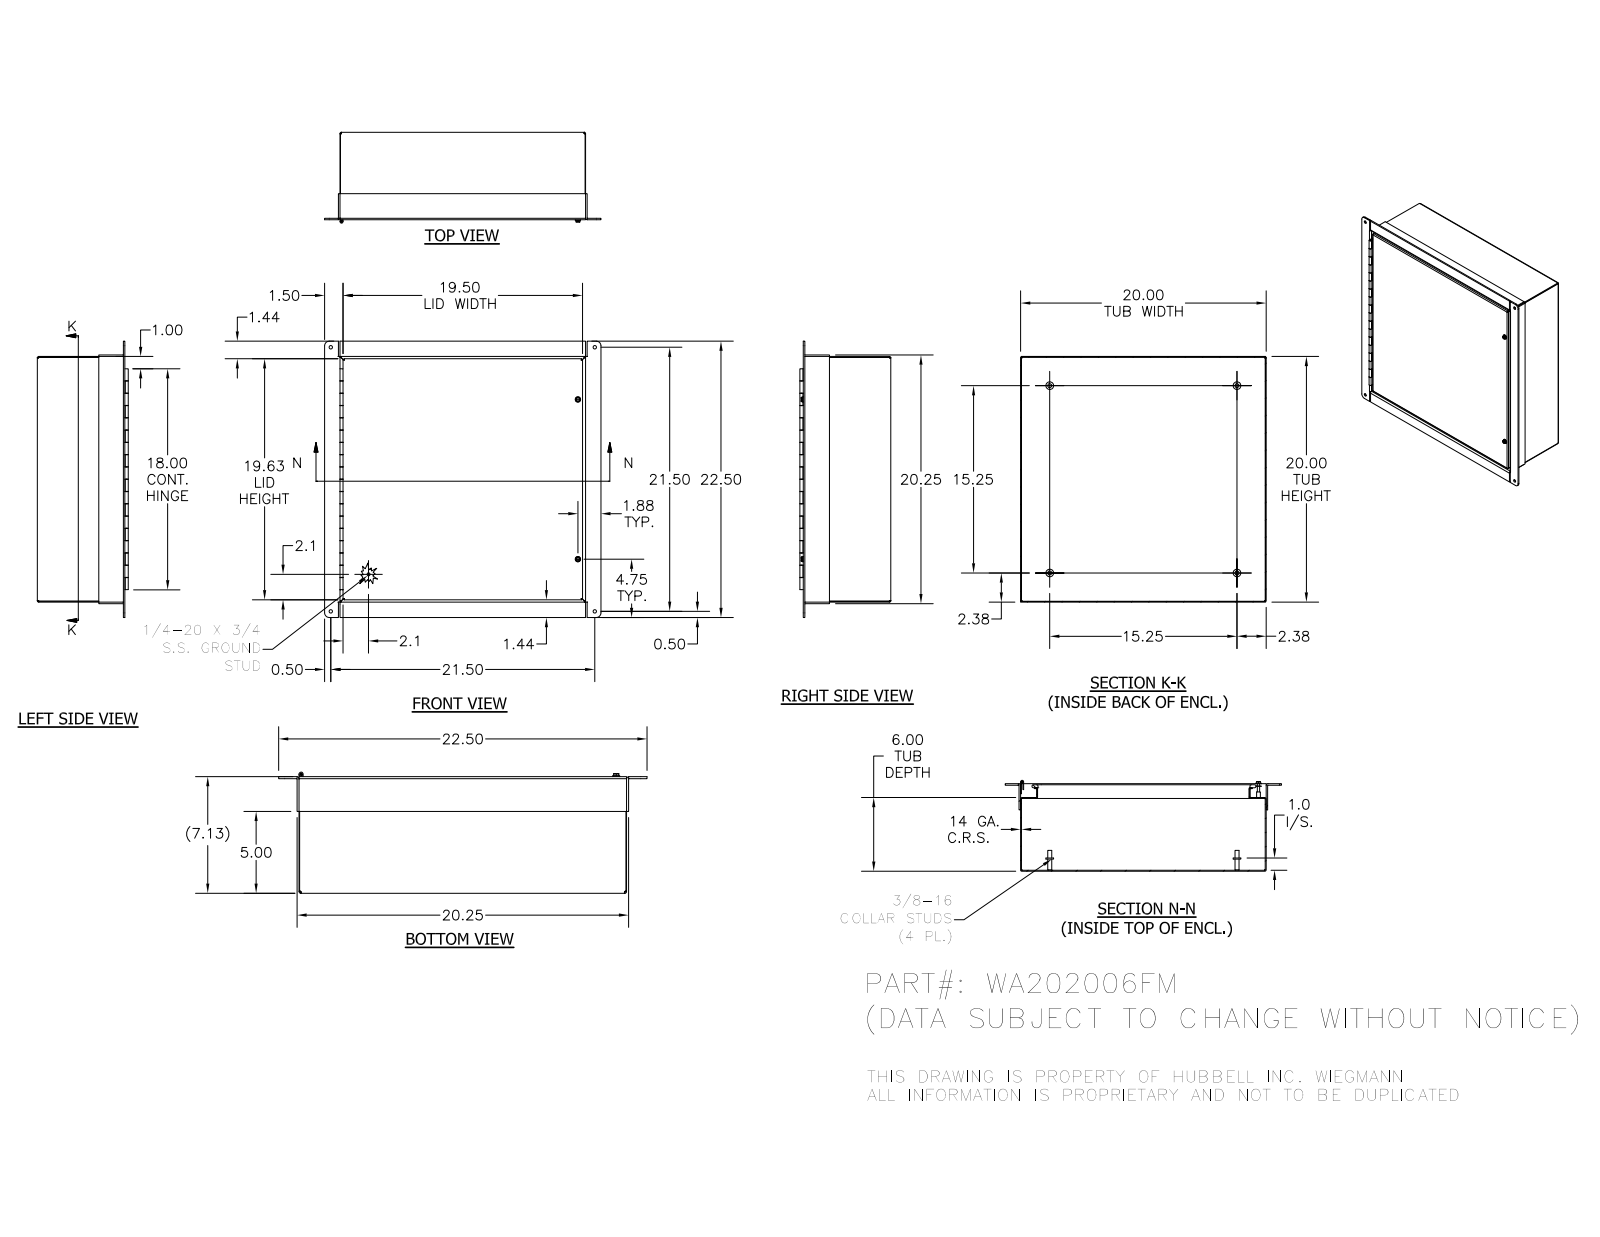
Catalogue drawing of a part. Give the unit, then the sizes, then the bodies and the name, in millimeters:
Units: millimetres
Overall size (bounding box): 571.5 × 571.5 × 187.96
Round holes (diameter × count): ⌀7.14 ×6, ⌀9.52 ×4, ⌀3.96 ×2, ⌀4.78 ×2, ⌀7.06 ×2, ⌀3.17 ×1
Round bosses / shafts (diameter × count): ⌀15.88 ×4, ⌀8.38 ×4, ⌀11.51 ×2, ⌀11.11 ×2, ⌀10.52 ×2, ⌀7.94 ×2, ⌀6.35 ×2, ⌀4.83 ×2
Partial cylindrical surfaces — rounded edges, fillets, slot ends (radius × count): R0.79 ×24, R2.67 ×20, R1.78 ×8, R3.17 ×8, R3.97 ×4, R9.53 ×4, R2.27 ×2
Main face-to-face distances: 1.88, 178.84, 506.12, 176.96, 180.72, 508, 504.24, 3.17, 150.52, 28.32
Hole centre spacings: 546.1, 113.46, 143.94, 439.54, 522.45, 673.26, 772.3, 143.95
Volume: 2 494 000 mm³ · Surface area: 2 375 000 mm²
Bodies: 23 solids, 601 faces (371 planar, 159 cylindrical, 71 other)
Part name (STEP PRODUCT): WA202006FMBKP; WA2020FMLID; 388116; H6010100T (+8 more)
STEP written by: Autodesk Inventor 2016 (AUTOMOTIVE_DESIGN)
